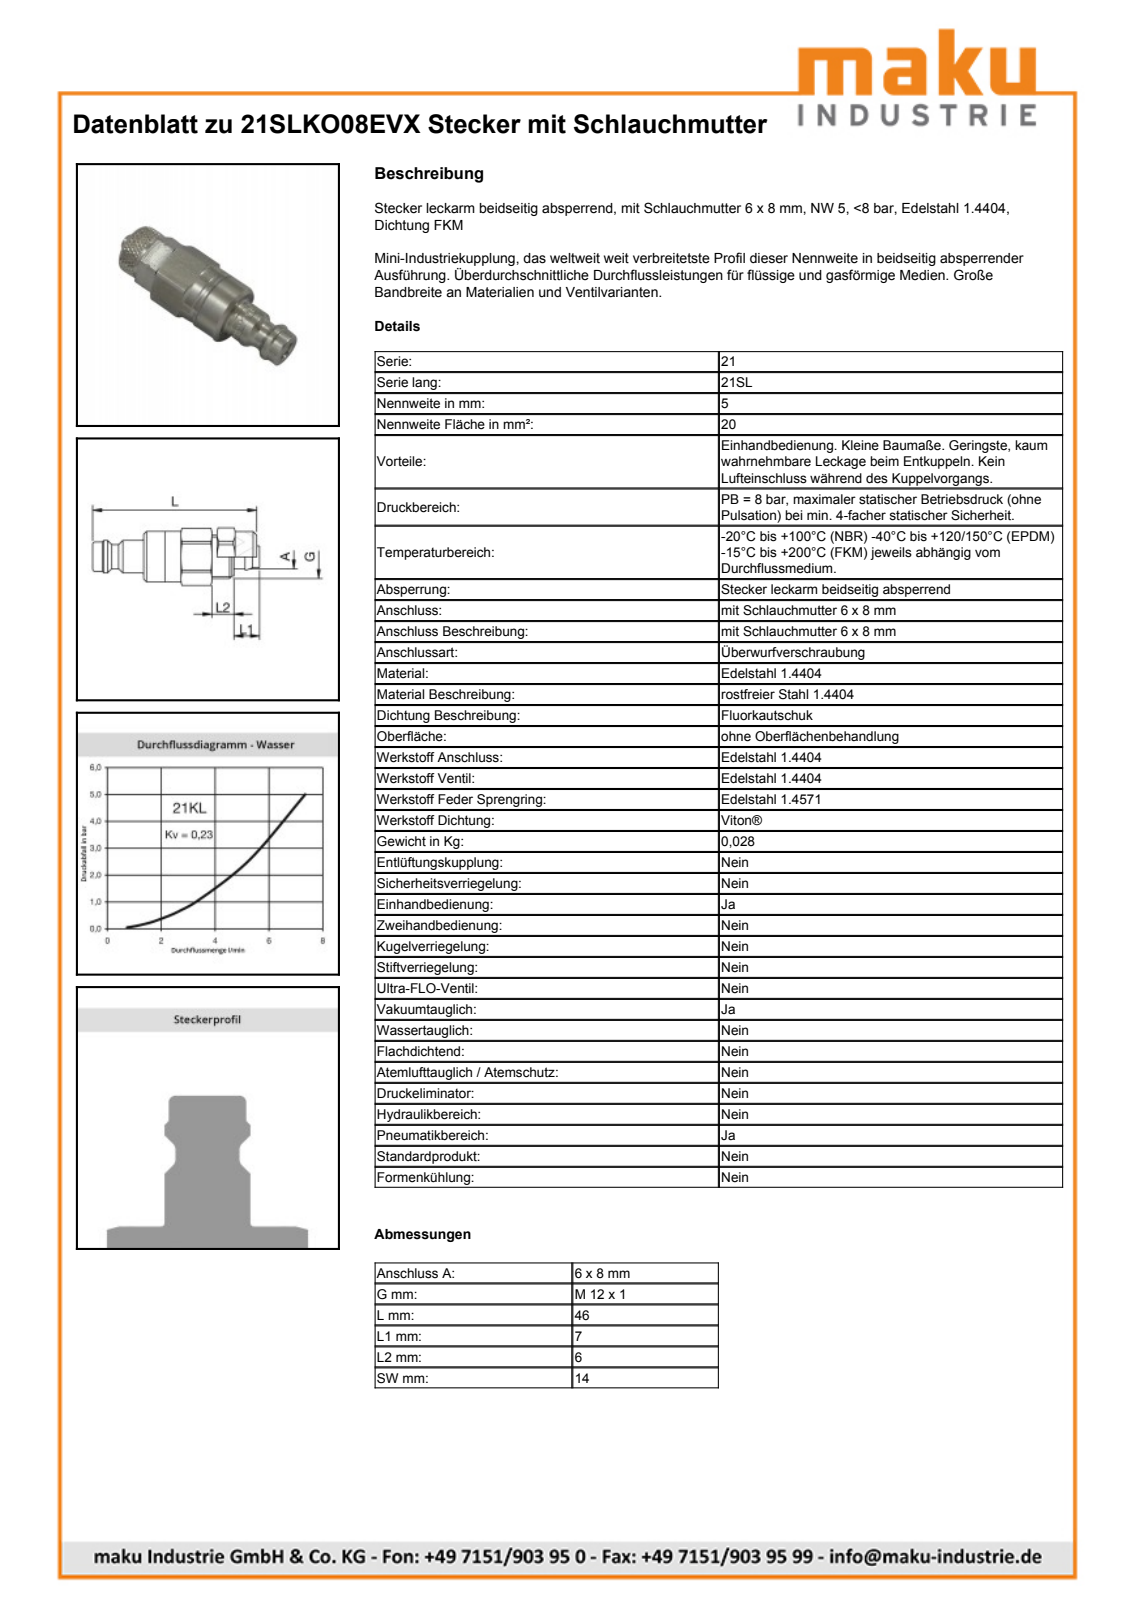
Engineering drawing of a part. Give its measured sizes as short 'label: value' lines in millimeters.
name: D109967; D105245; D105915; D105918
written by: Autodesk Inventor 2013 (AUTOMOTIVE_DESIGN)
unit: mm
bodies: 3 solids, 116 faces (25 planar, 36 cylindrical, 55 other)
size: 46 × 15.63 × 15.12
volume: 3 351 mm³; area: 4 500 mm²
holes: 1× ⌀4.2, 1× ⌀4.9, 1× ⌀5.5, 1× ⌀7.2, 1× ⌀9.5, 1× ⌀10.45, 1× ⌀11, 1× ⌀12.1, 1× ⌀12.5, 1× ⌀12.6
bosses: 1× ⌀14, 1× ⌀12, 1× ⌀10.85, 1× ⌀10.4, 1× ⌀9, 1× ⌀8.1, 1× ⌀6.7, 1× ⌀6.05
rounds: 1× R7.75, 1× R7.9
face distances: 14, 13.9, 11, 6, 9.9, 18.9, 7.9, 5, 12.1, 12.8
